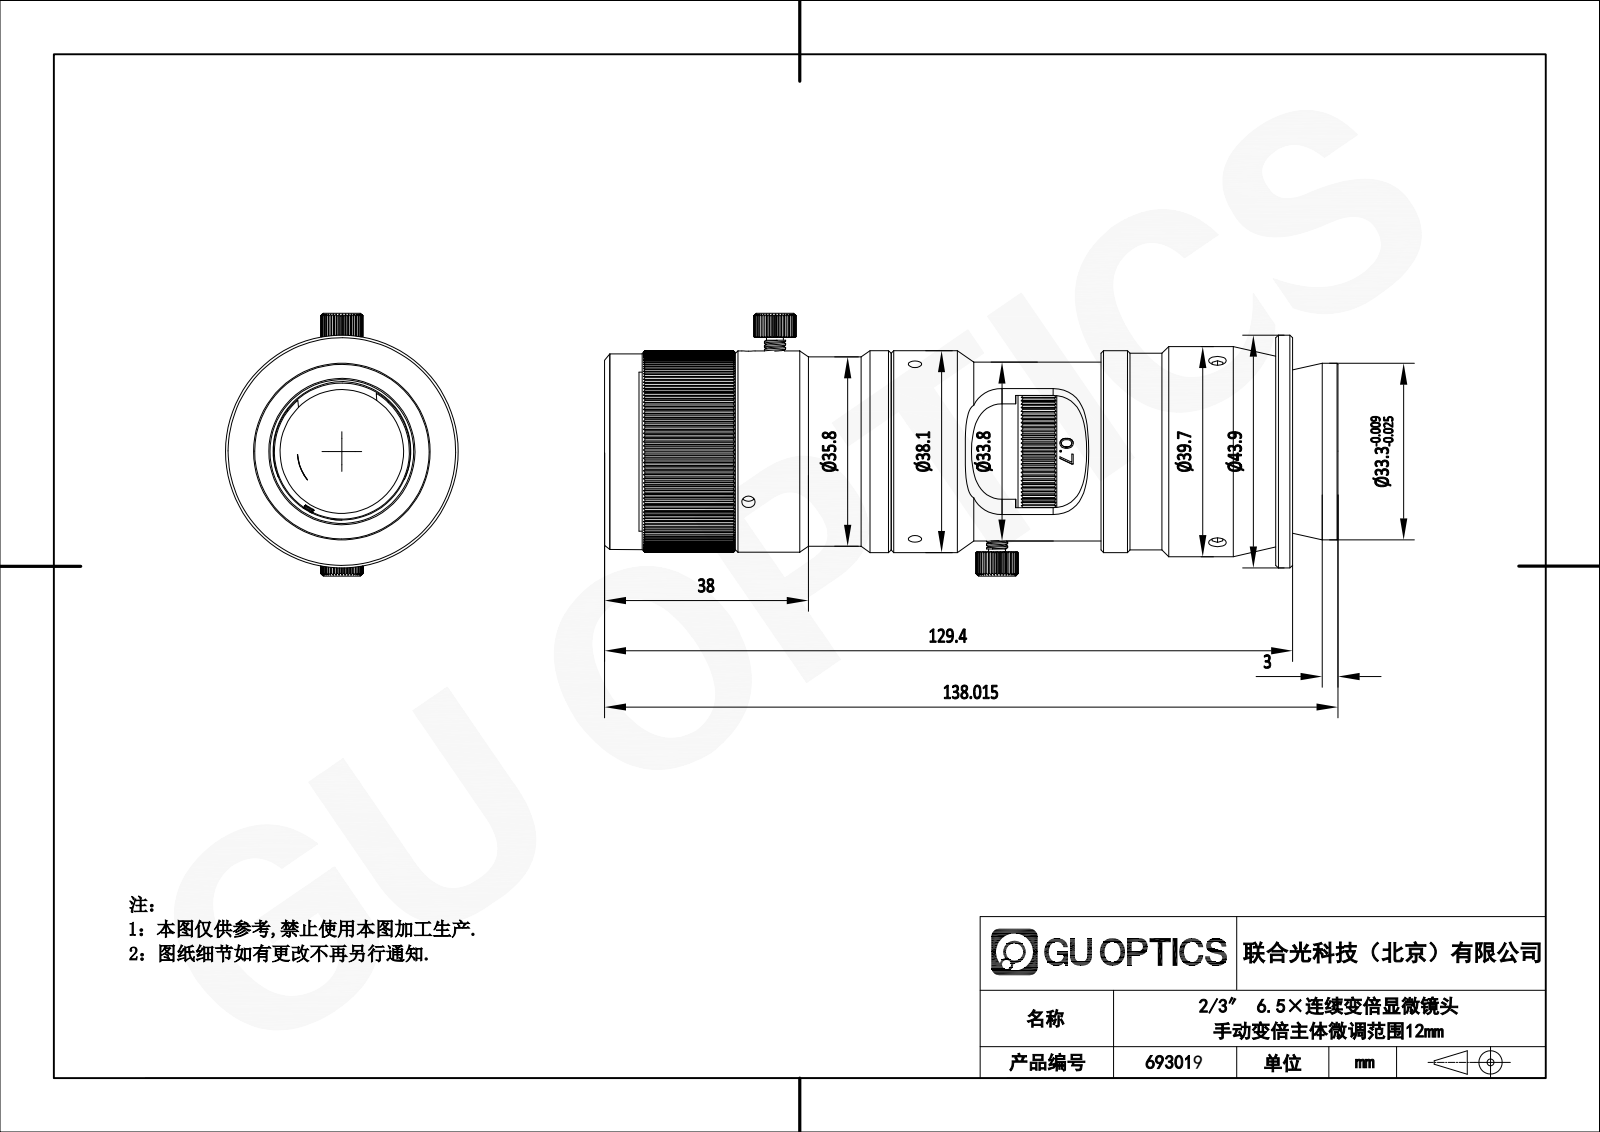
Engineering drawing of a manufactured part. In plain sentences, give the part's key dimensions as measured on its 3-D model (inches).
The part is named "693019". Its 3-D file was written by "SolidWorks 2020 (CONFIG_CONTROL_DESIGN)". It is 0 solids with 1790 faces: 911 planar, 482 cylindrical and 397 other. Overall it measures 5.43 by 1.952 by 1.73 inches. Round holes: 6 of diameter 0.098, 3 of diameter 0.13, 2 of diameter 0.067, 2 of diameter 0.12, 1 of diameter 0.083, 1 of diameter 0.126, 1 of diameter 0.921, 1 of diameter 1.004, 1 of diameter 1.018, 1 of diameter 1.024, 1 of diameter 1.043, 1 of diameter 1.063. Round bosses or shafts: 7 of diameter 0.079, 5 of diameter 0.157, 2 of diameter 0.126, 1 of diameter 1.73, 1 of diameter 1.561, 1 of diameter 1.5, 1 of diameter 1.496, 1 of diameter 1.461. Partial cylindrical surfaces (rounded edges, fillets, slot ends): 4 of radius 0.276, 2 of radius 0.069, 2 of radius 0.157, 1 of radius 0.33, 1 of radius 0.402, 1 of radius 0.587, 1 of radius 0.61, 1 of radius 0.674. The main face-to-face distances are 0.125, 3.842, 3.967, 1.044, 1.043, 0.983, 2.858, 2.983, 1.424, 1.342. The hole center spacings are 2.248, 0.197, 0.906, 1.342, 1.651, 1.848.
